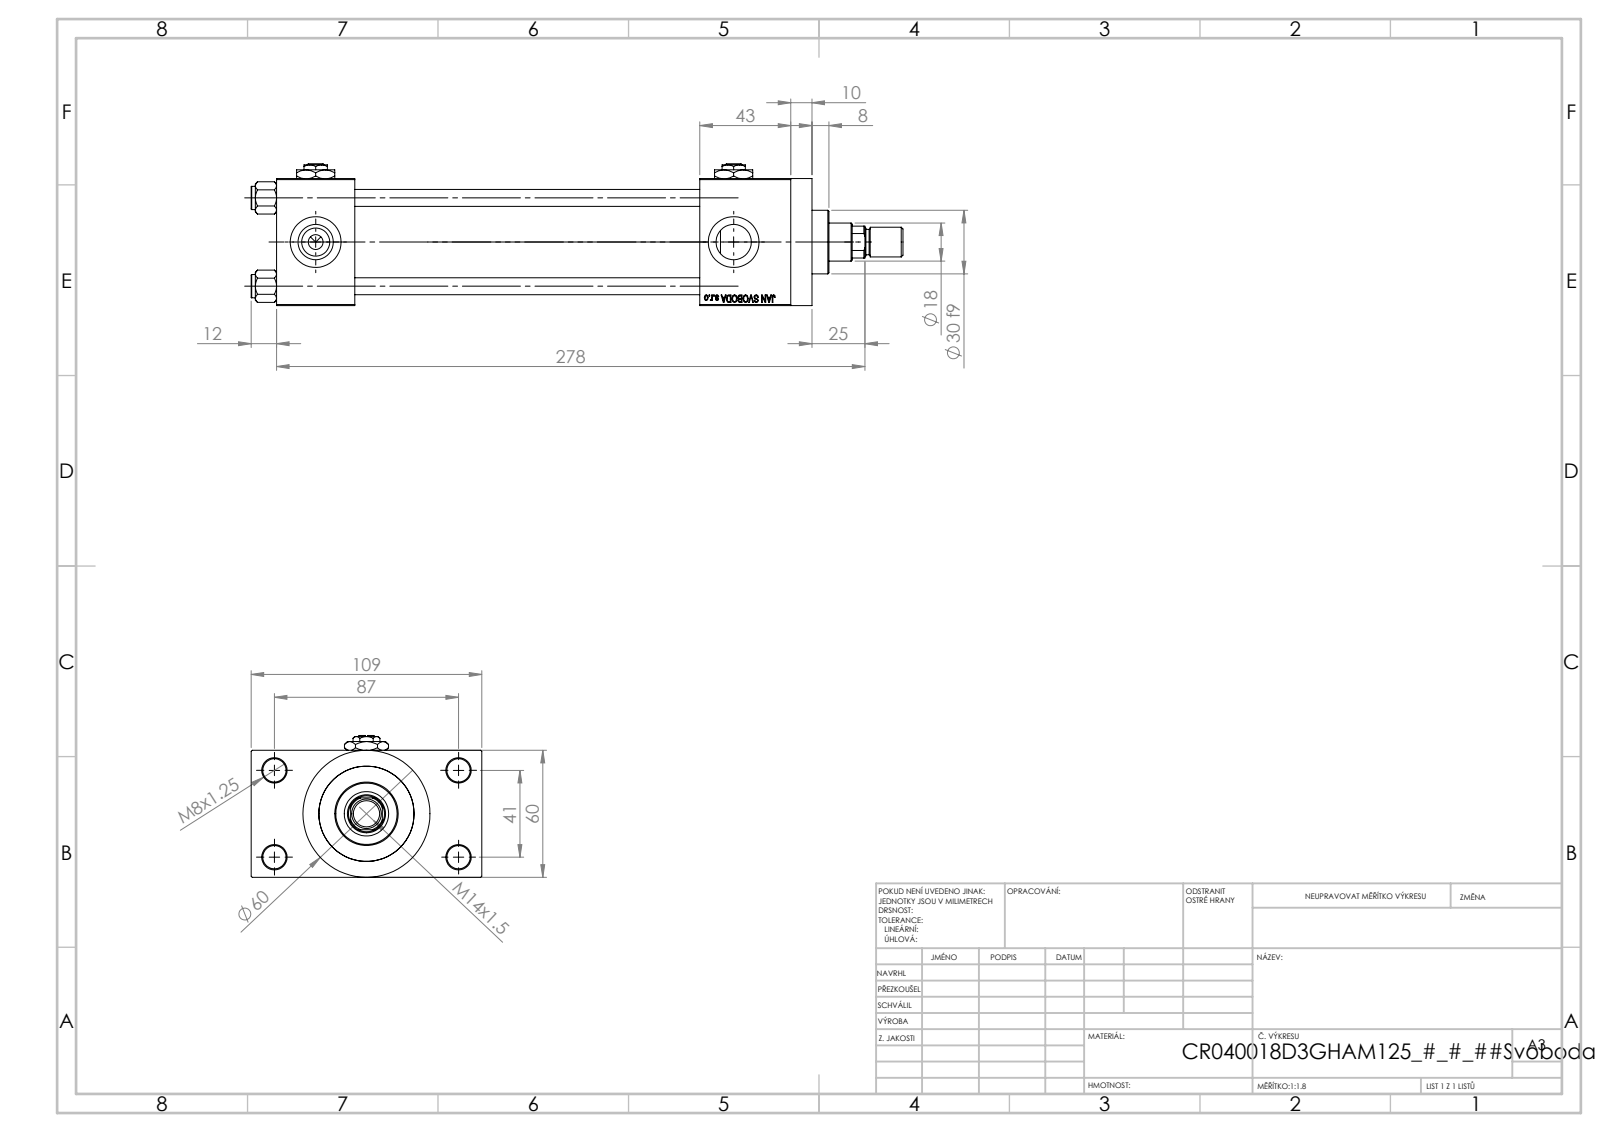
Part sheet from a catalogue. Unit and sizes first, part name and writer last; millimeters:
Units: millimetres
Overall size (bounding box): 308 × 109 × 67
Round holes (diameter × count): ⌀8 ×4, ⌀11 ×4, ⌀16.66 ×4, ⌀24 ×4, ⌀7 ×3, ⌀8.5 ×1, ⌀18 ×1, ⌀21 ×1, ⌀31 ×1, ⌀40 ×1, ⌀45 ×1
Round bosses / shafts (diameter × count): ⌀11 ×4, ⌀60 ×1, ⌀46 ×1, ⌀30 ×1, ⌀14 ×1, ⌀12 ×1
Partial cylindrical surfaces — rounded edges, fillets, slot ends (radius × count): R8.5 ×1
Main face-to-face distances: 60, 163, 24.5, 84.5, 37, 200, 43, 243, 206, 53
Hole centre spacings: 22.65, 29.49, 41.7, 47.15, 48.09, 64.35, 76.49, 41
Volume: 603 393 mm³ · Surface area: 171 180 mm²
Bodies: 14 solids, 1219 faces (550 planar, 103 cylindrical, 566 other)
Part name (STEP PRODUCT): V215CR_VCP_D; Zatka_pro_OIL_PORT; V215CR_D_TYCINKA; V215_VC_A (+3 more)
STEP written by: SolidWorks 2019 (CONFIG_CONTROL_DESIGN)
